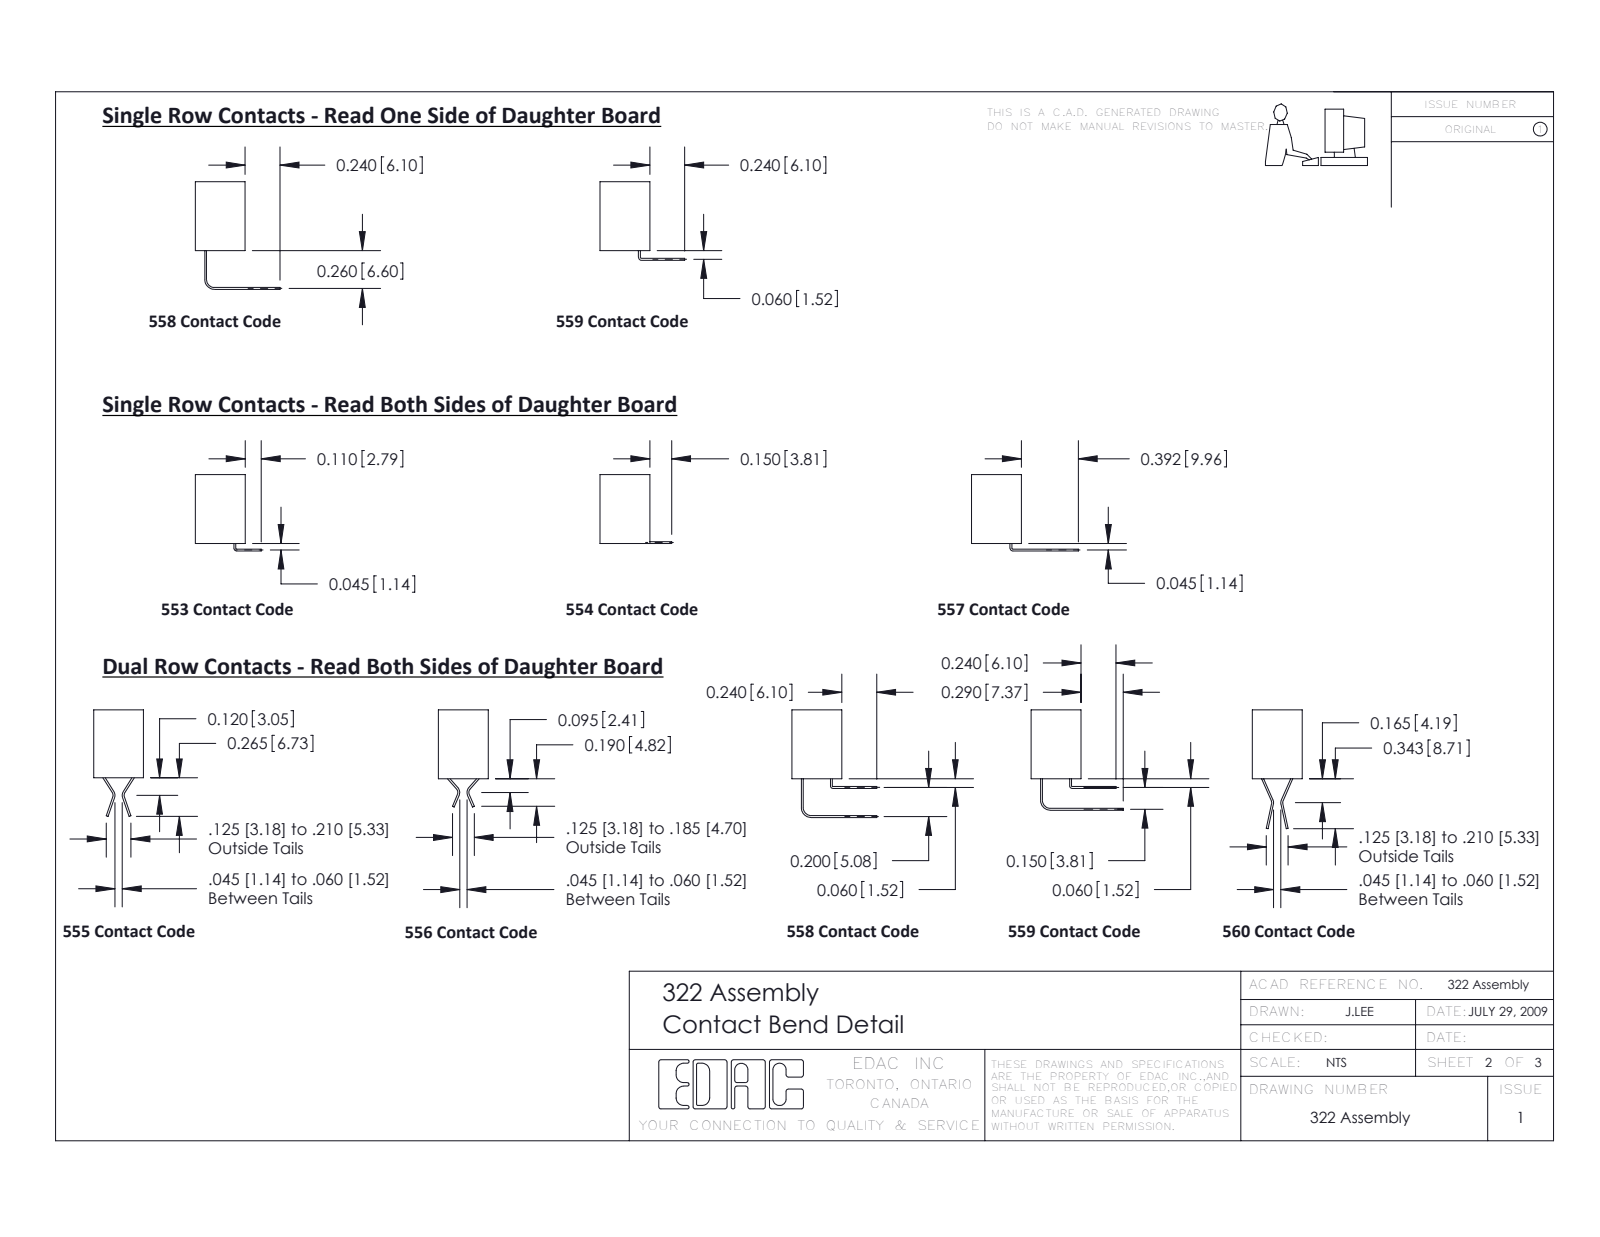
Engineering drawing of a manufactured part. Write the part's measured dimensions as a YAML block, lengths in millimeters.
part_name: "307-290-001_520; 322 Part; 307-250-006-100_307-250-006-100; 322-044-520-258"
step_written_by: "SolidWorks 2016 (CONFIG_CONTROL_DESIGN)"
units: millimeters
bodies: {solids: 5, faces: 673, planar: 541, cylindrical: 128, other: 4}
overall_size: [123.8, 81.6, 8.7]
volume: 15600
surface_area: 14440
round_holes:
  - {diameter: 2.3, count: 2}
  - {diameter: 4, count: 2}
round_bosses_or_shafts:
  - {diameter: 3.8, count: 2}
partial_cylinders:
  - {radius: 0.3, count: 22}
  - {radius: 0.2, count: 6}
  - {radius: 1, count: 6}
  - {radius: 1.6, count: 4}
  - {radius: 0.5, count: 3}
  - {radius: 0.8, count: 3}
  - {radius: 0.3, count: 2}
  - {radius: 0.6, count: 2}
face_to_face_distances: [8.7, 1.6, 7.1, 3.4, 5.3, 1.8, 3.7, 3.3, 5.4, 1.7]
hole_center_spacings: [102.4]
